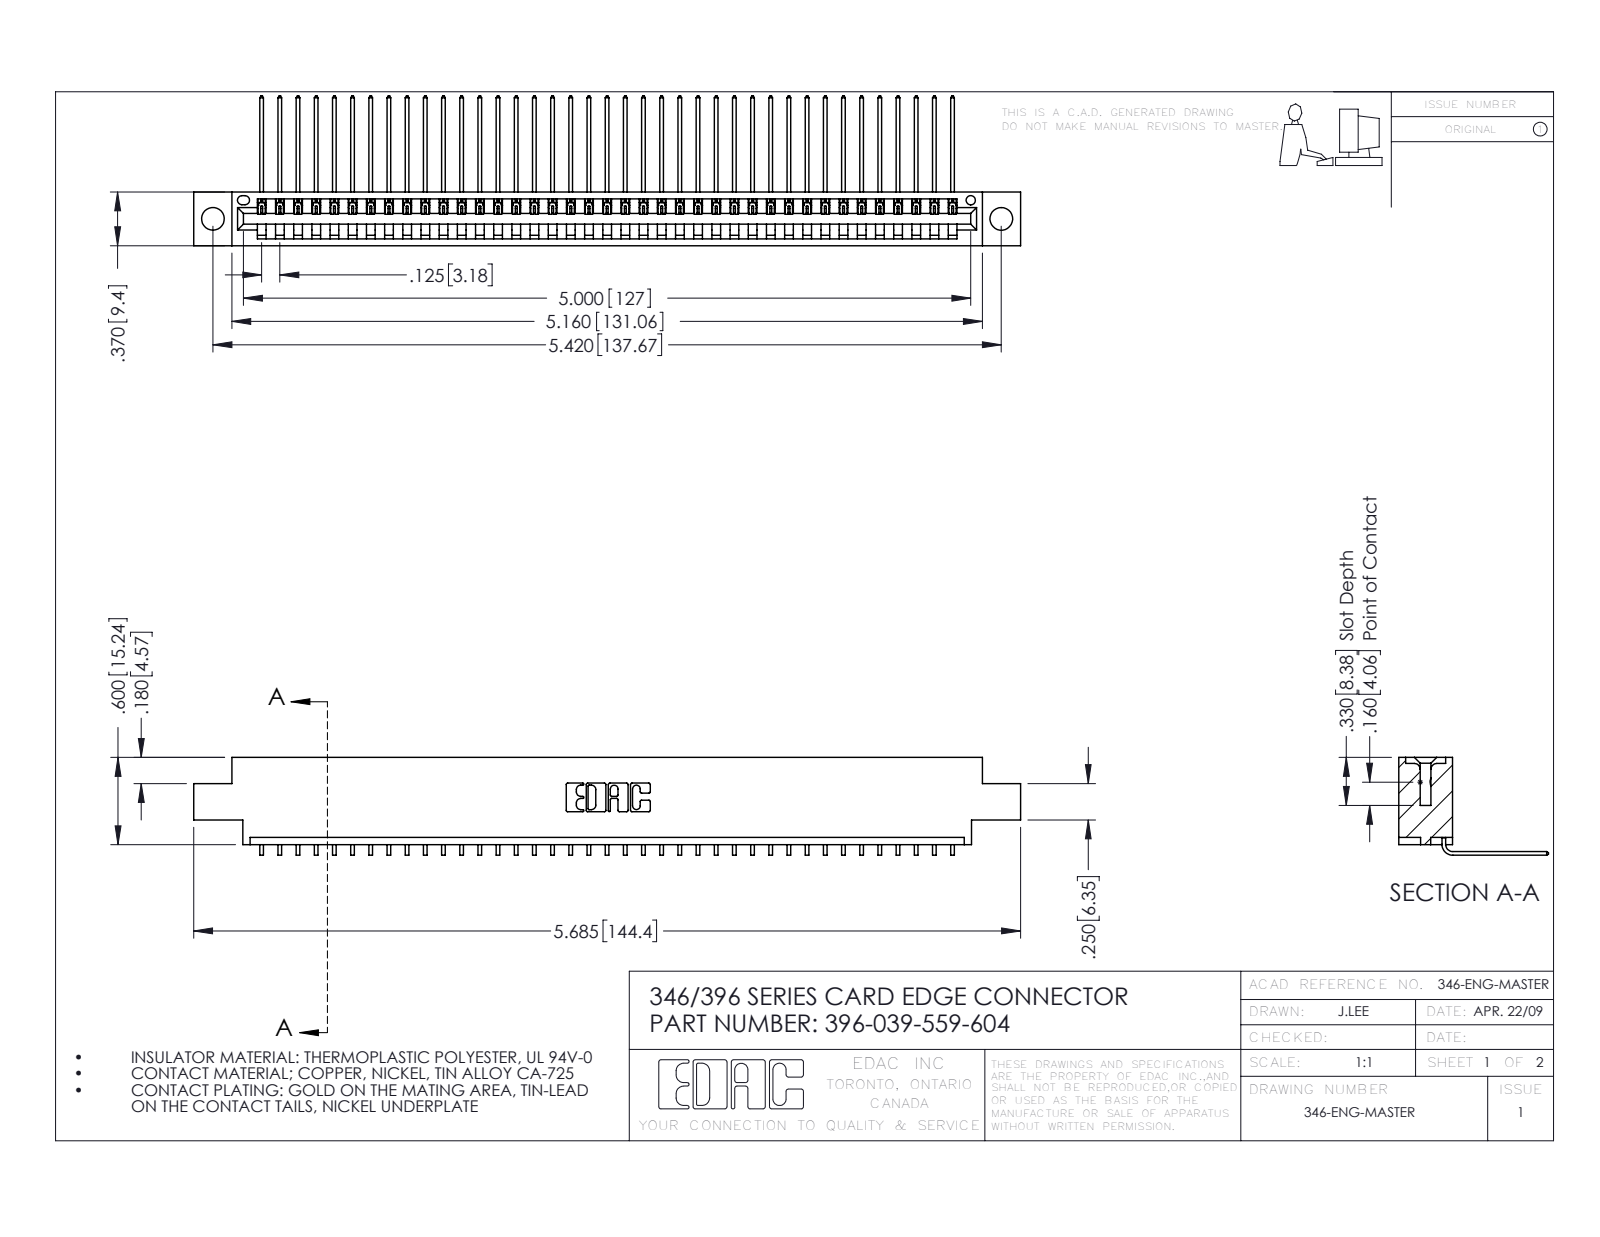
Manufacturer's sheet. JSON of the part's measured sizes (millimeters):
{"part_name": "346 Part_0.170 Offset - 0.156 Dia-TH; 396-039-559-604; 345-292-001_558 559 Tail - 1", "step_written_by": "SolidWorks 2016 (CONFIG_CONTROL_DESIGN)", "units": "millimeters", "bodies": {"solids": 40, "faces": 2466, "planar": 1718, "cylindrical": 748, "other": 0}, "overall_size": [144.4, 26.2, 17.1], "volume_mm3": 13700, "surface_area_mm2": 17820, "round_holes": [[4, 2], [1.6, 1]], "partial_cylinders_radius": [[0.2, 78], [0.3, 22], [0.2, 6], [0.8, 6], [0.7, 3], [0.8, 2], [1, 2], [0.4, 1]], "face_to_face_distances": [1.2, 8.2, 9.4, 0.6, 6.4, 1.8, 7.6, 3.8, 5.6, 2.5], "hole_center_spacings": [6.2, 132.4, 137.7]}
